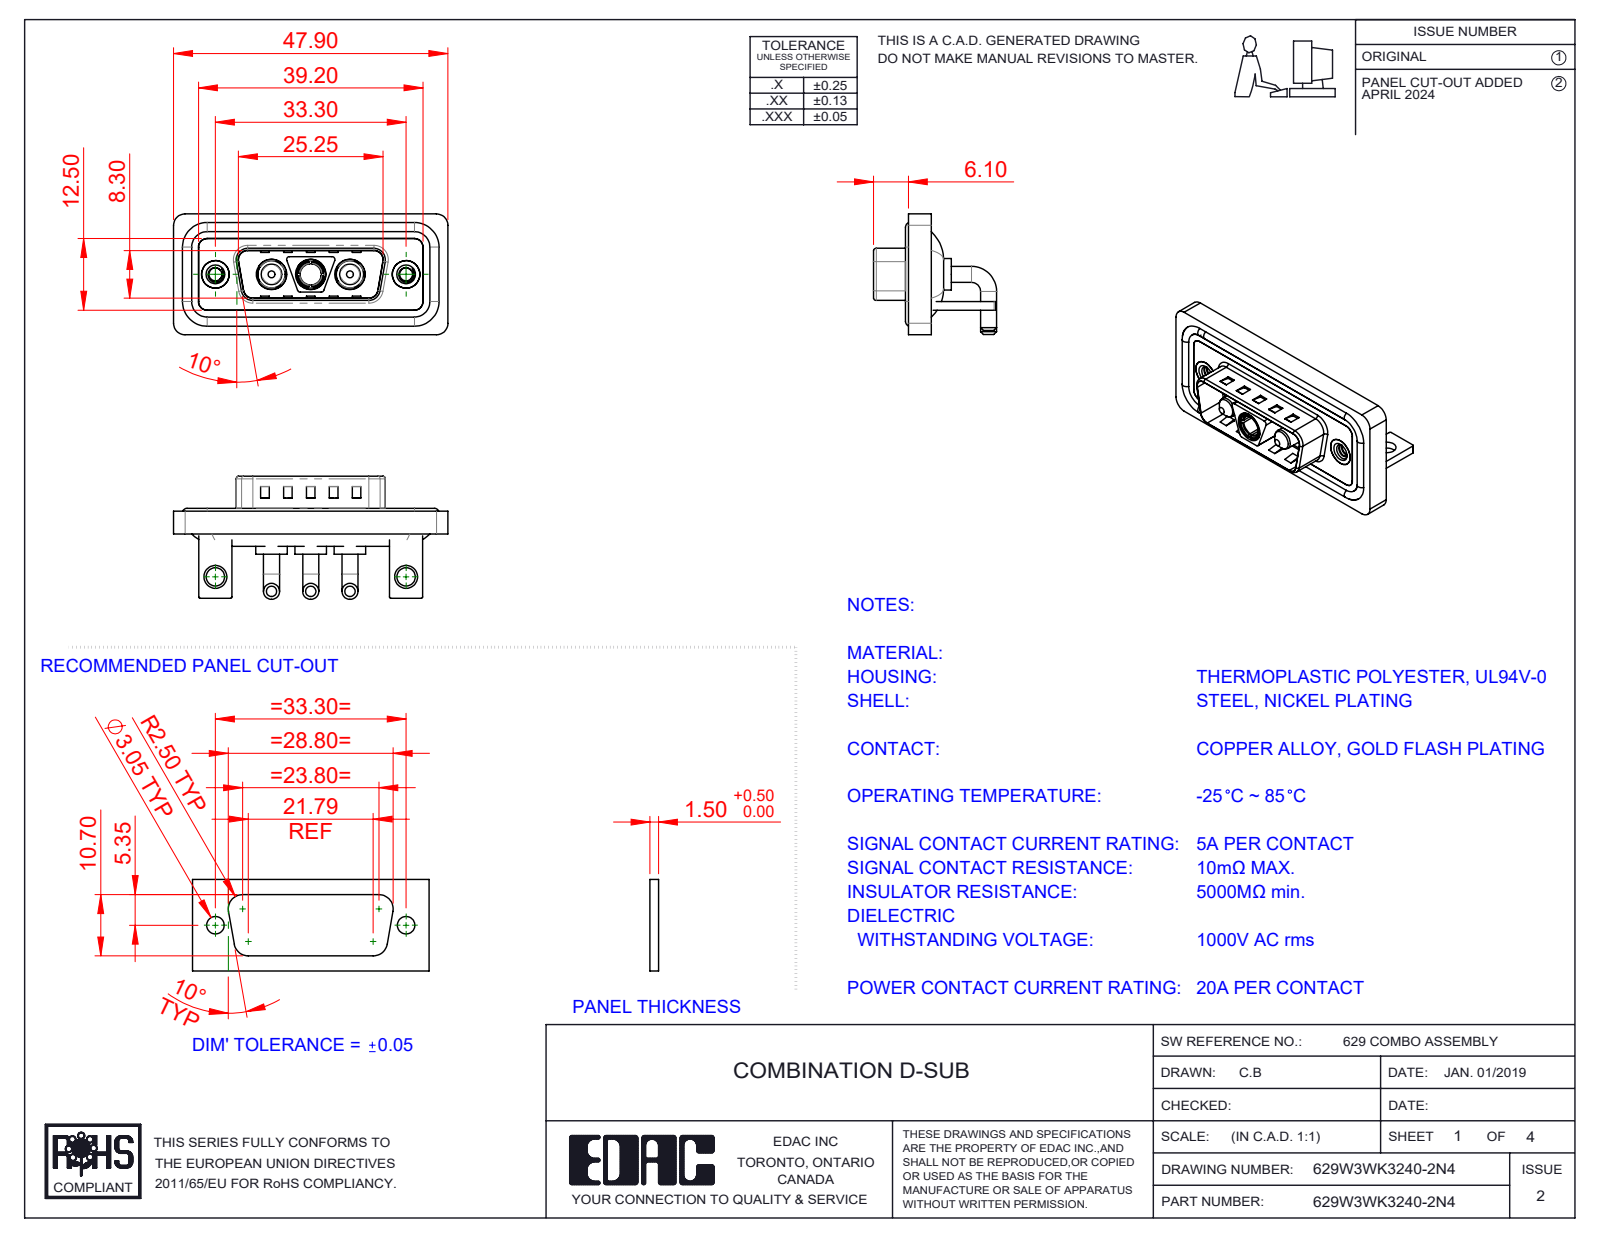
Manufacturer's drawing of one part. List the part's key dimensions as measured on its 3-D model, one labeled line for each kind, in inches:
Part name (STEP PRODUCT): 629Combo Waterproof Housing_15 Contacts; Power Socket_20A RA; 629Combo Shell Front_15 Contacts; 629W3WK3240-2N4 (+5 more)
STEP written by: SolidWorks 2023 (CONFIG_CONTROL_DESIGN)
Units: inches
Bodies: 15 solids, 661 faces (251 planar, 274 cylindrical, 136 other)
Overall size (bounding box): 1.886 × 0.846 × 0.831
Volume: 0.376 in³ · Surface area: 15.5 in²
Round holes (diameter × count): ⌀0.191 ×3, ⌀0.209 ×3, ⌀0.089 ×2, ⌀0.126 ×2, ⌀0.157 ×2, ⌀0.189 ×2, ⌀0.197 ×2, ⌀0.146 ×1
Round bosses / shafts (diameter × count): ⌀0.11 ×6, ⌀0.063 ×4, ⌀0.217 ×3, ⌀0.205 ×3, ⌀0.187 ×3, ⌀0.148 ×3, ⌀0.193 ×2, ⌀0.142 ×2
Partial cylindrical surfaces — rounded edges, fillets, slot ends (radius × count): R0.079 ×21, R0.059 ×18, R0.01 ×16, R0.02 ×13, R0.063 ×8, R0.024 ×4, R0.026 ×4, R0.035 ×4
Main face-to-face distances: 0.016, 0.059, 0.031, 0.114, 0.043, 0.083, 0.146, 0.063, 0.047, 0.177
Hole centre spacings: 0.27, 0.386, 0.656, 0.925, 1.311, 0.539
